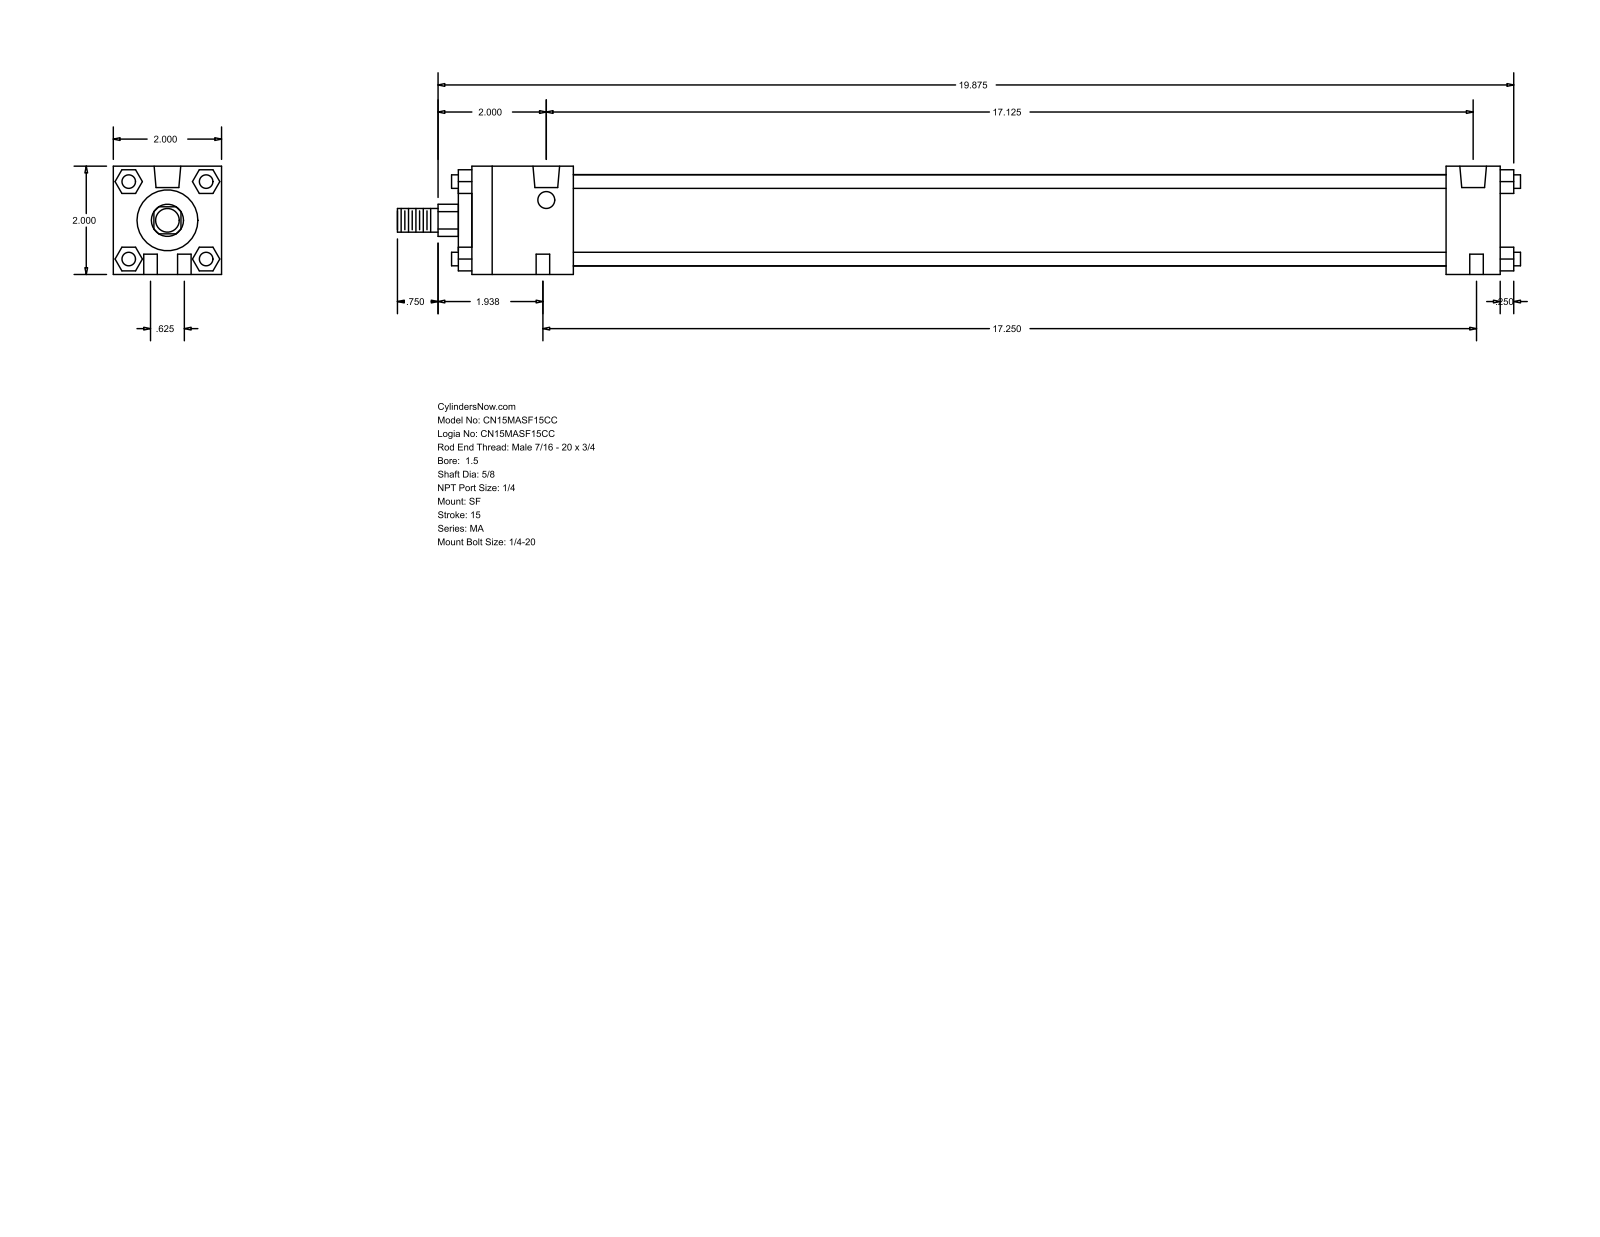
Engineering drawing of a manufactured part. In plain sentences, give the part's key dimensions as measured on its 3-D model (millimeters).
The part is named "MA_SF__0150_0.625". Its 3-D file was written by "GSSL Pune (CONFIG_CONTROL_DESIGN)". It is 0 solids with 124 faces: 94 planar, 30 cylindrical and 0 other. Overall it measures 527.05 by 50.8 by 50.8 millimeters. Round holes: 4 of diameter 6.35, 2 of diameter 7.94, 2 of diameter 12.49. Round bosses or shafts: 4 of diameter 6.35, 1 of diameter 42.93, 1 of diameter 28.57, 1 of diameter 15.88, 1 of diameter 11.11. Partial cylindrical surfaces (rounded edges, fillets, slot ends): 1 of radius 7.54. The main face-to-face distances are 50.8, 482.6, 47.62, 457.19, 409.57, 434.98, 25.41, 6.35, 53.97, 463.54. The hole center spacings are 8.1, 436.63, 15.88, 434.97, 438.15, 438.44.
